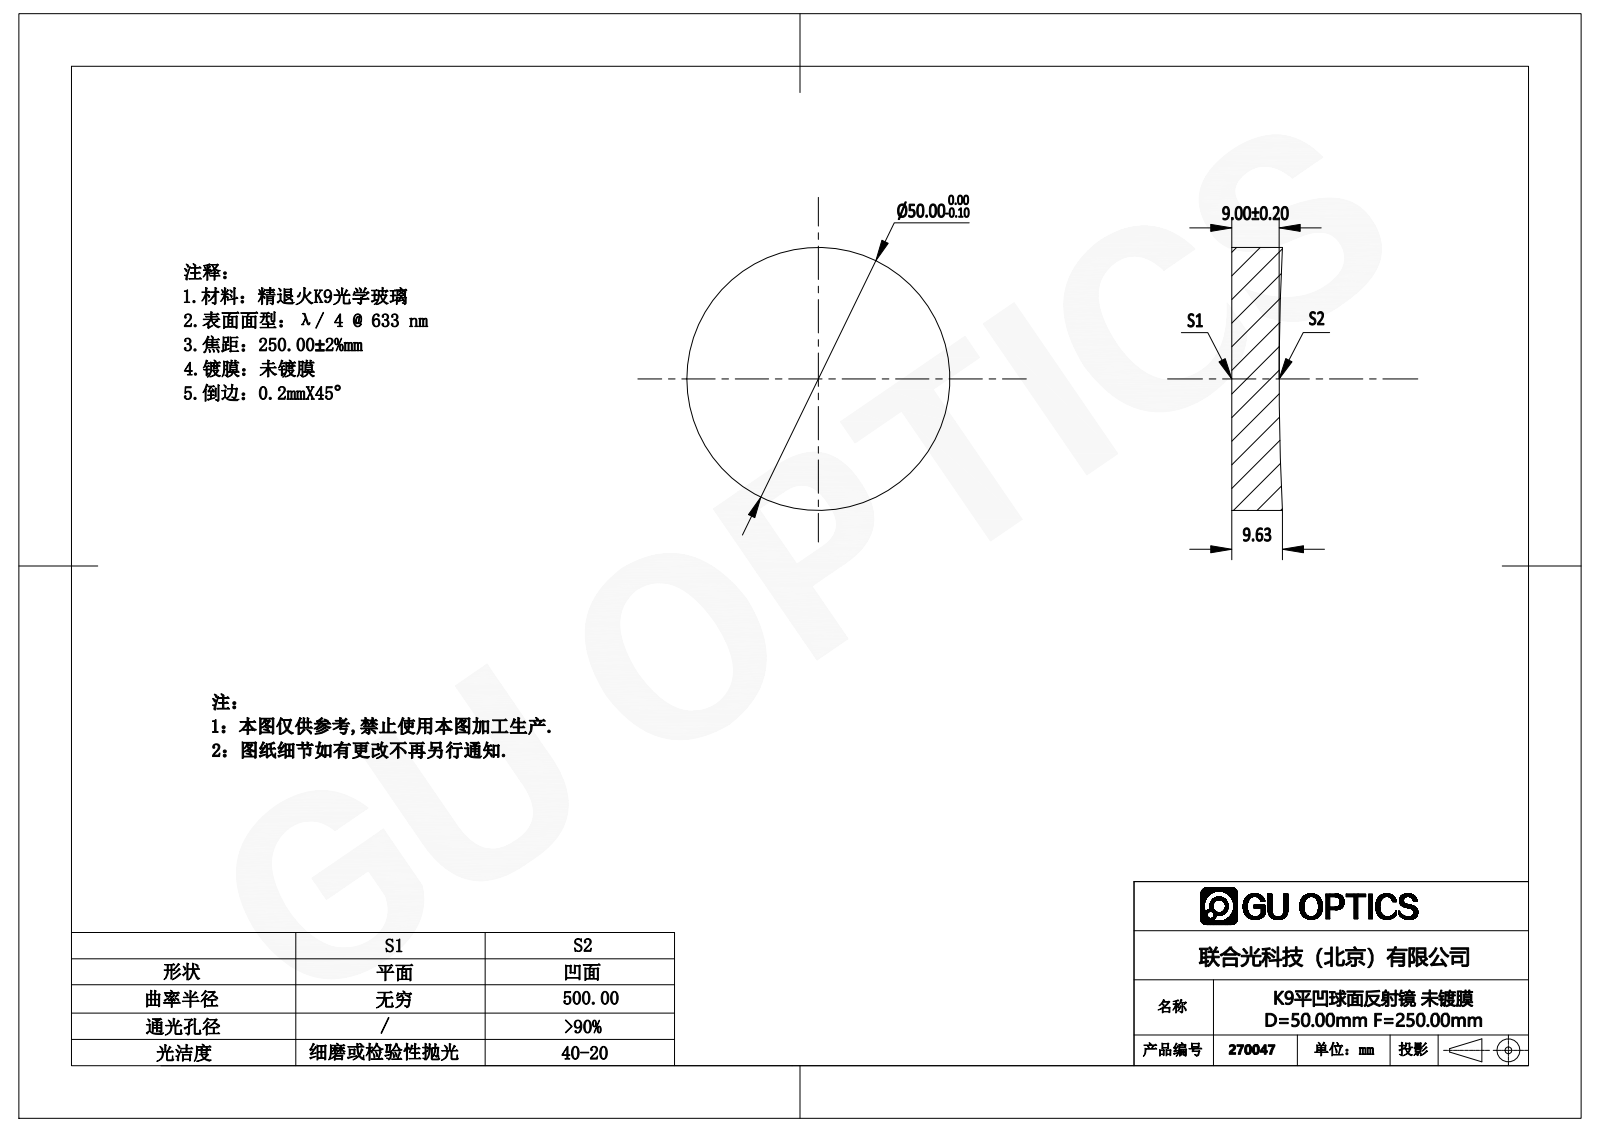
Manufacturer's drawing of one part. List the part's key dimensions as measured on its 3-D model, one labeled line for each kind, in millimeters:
Part name (STEP PRODUCT): 270047
STEP written by: SolidWorks 2016 (AUTOMOTIVE_DESIGN)
Units: millimetres
Bodies: 1 solid, 5 faces (1 planar, 2 cylindrical, 2 other)
Overall size (bounding box): 50 × 50 × 9.62
Volume: 18 285 mm³ · Surface area: 5 440 mm²
Round bosses / shafts (diameter × count): ⌀50 ×1
